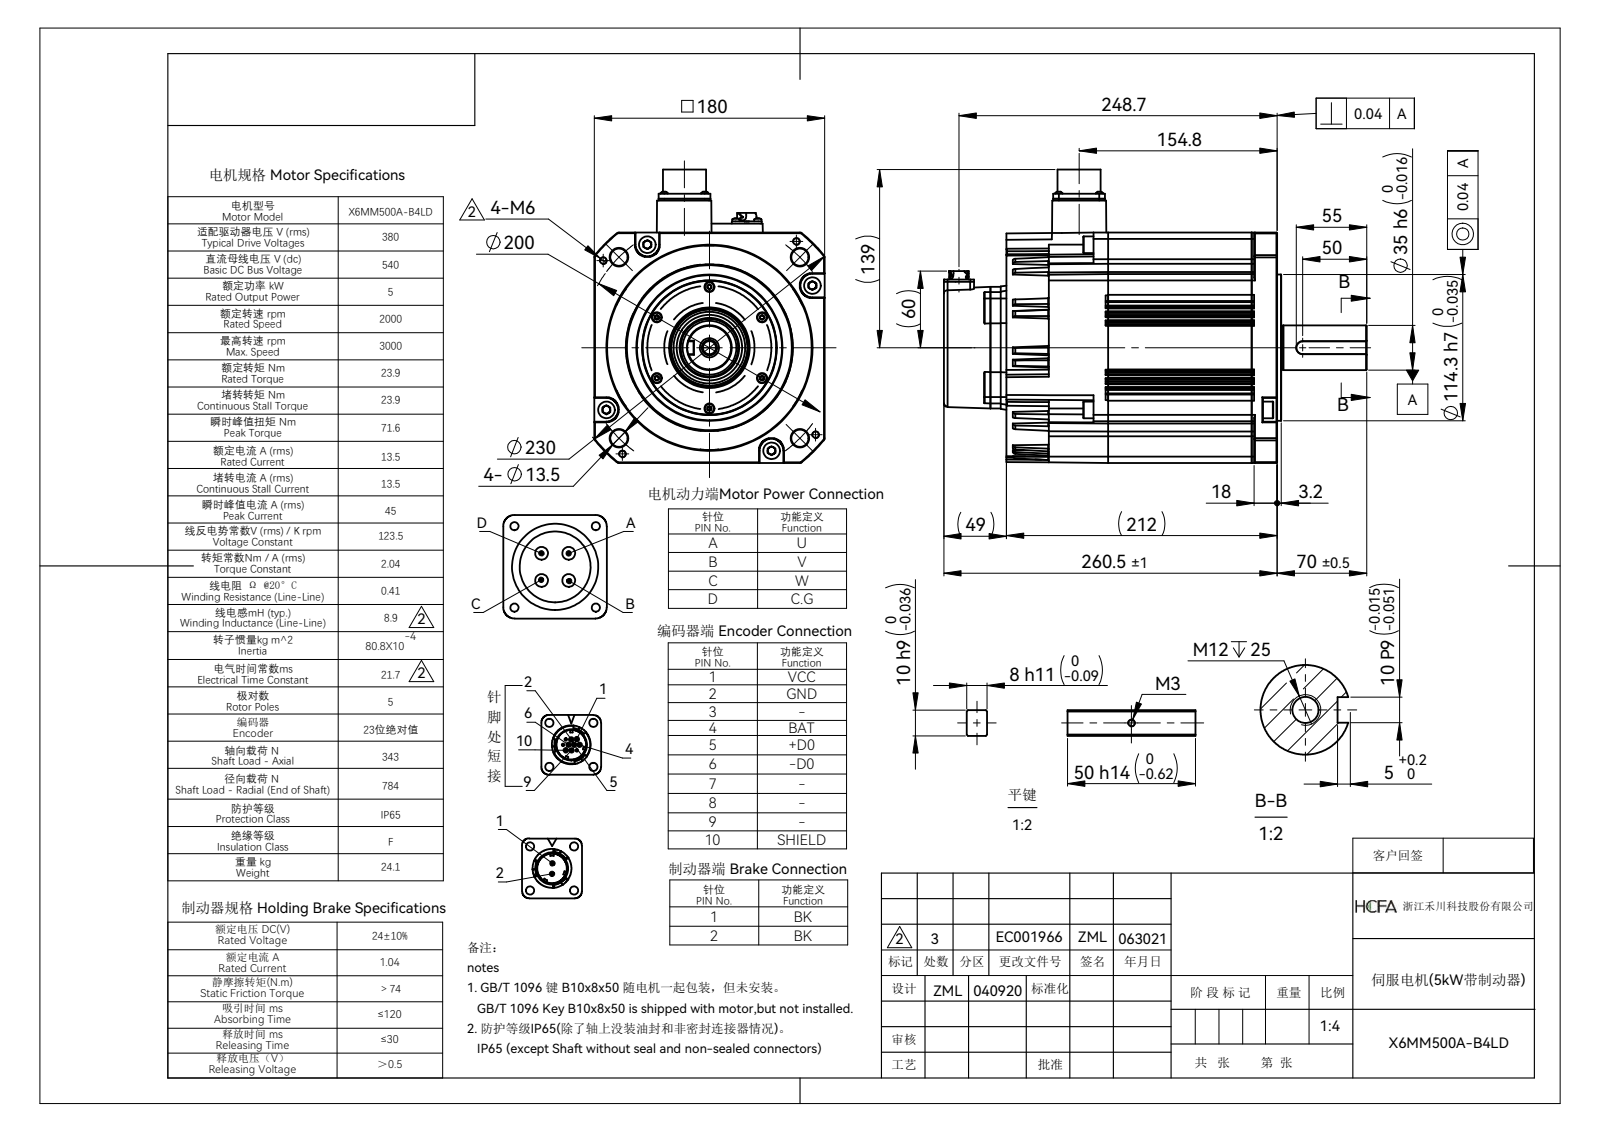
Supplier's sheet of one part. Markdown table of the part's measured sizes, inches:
| quantity | value |
| --- | --- |
| part name | SV-X6MM500A-B4LD |
| STEP written by | SolidWorks 2016 (CONFIG_CONTROL_DESIGN) |
| units | inches |
| bodies | 12 solids, 2502 faces (896 planar, 911 cylindrical, 695 other) |
| overall size | 13.012 × 9.026 × 7.087 |
| volume | 381.9 in³ |
| surface area | 466.1 in² |
| round holes (diameter × count) | 0.098 × 20, 0.126 × 12, 0.13 × 5, 0.118 × 4, 0.138 × 4, 0.256 × 4, 0.268 × 4, 0.354 × 4, 0.531 × 4, 0.48 × 3, 0.63 × 3, 0.039 × 2 |
| round bosses / shafts (diameter × count) | 0.118 × 8, 0.512 × 5, 0.315 × 4, 0.224 × 4, 0.22 × 4, 0.197 × 4, 0.598 × 2, 0.059 × 2 |
| partial cylindrical surfaces (radius × count) | 0.02 × 98, 0.039 × 42, 0.197 × 29, 0.079 × 18, 0.118 × 12, 0.157 × 6, 0.11 × 4, 0.122 × 4 |
| main face-to-face distances | 7.087, 1.28, 5.807, 8.327, 8.453, 0.126, 4.528, 1.929, 10.256, 10.382 |
| hole center spacings | 0.479, 0.677, 4.493, 3.874, 0.235, 0.423, 0.542, 0.885 |
